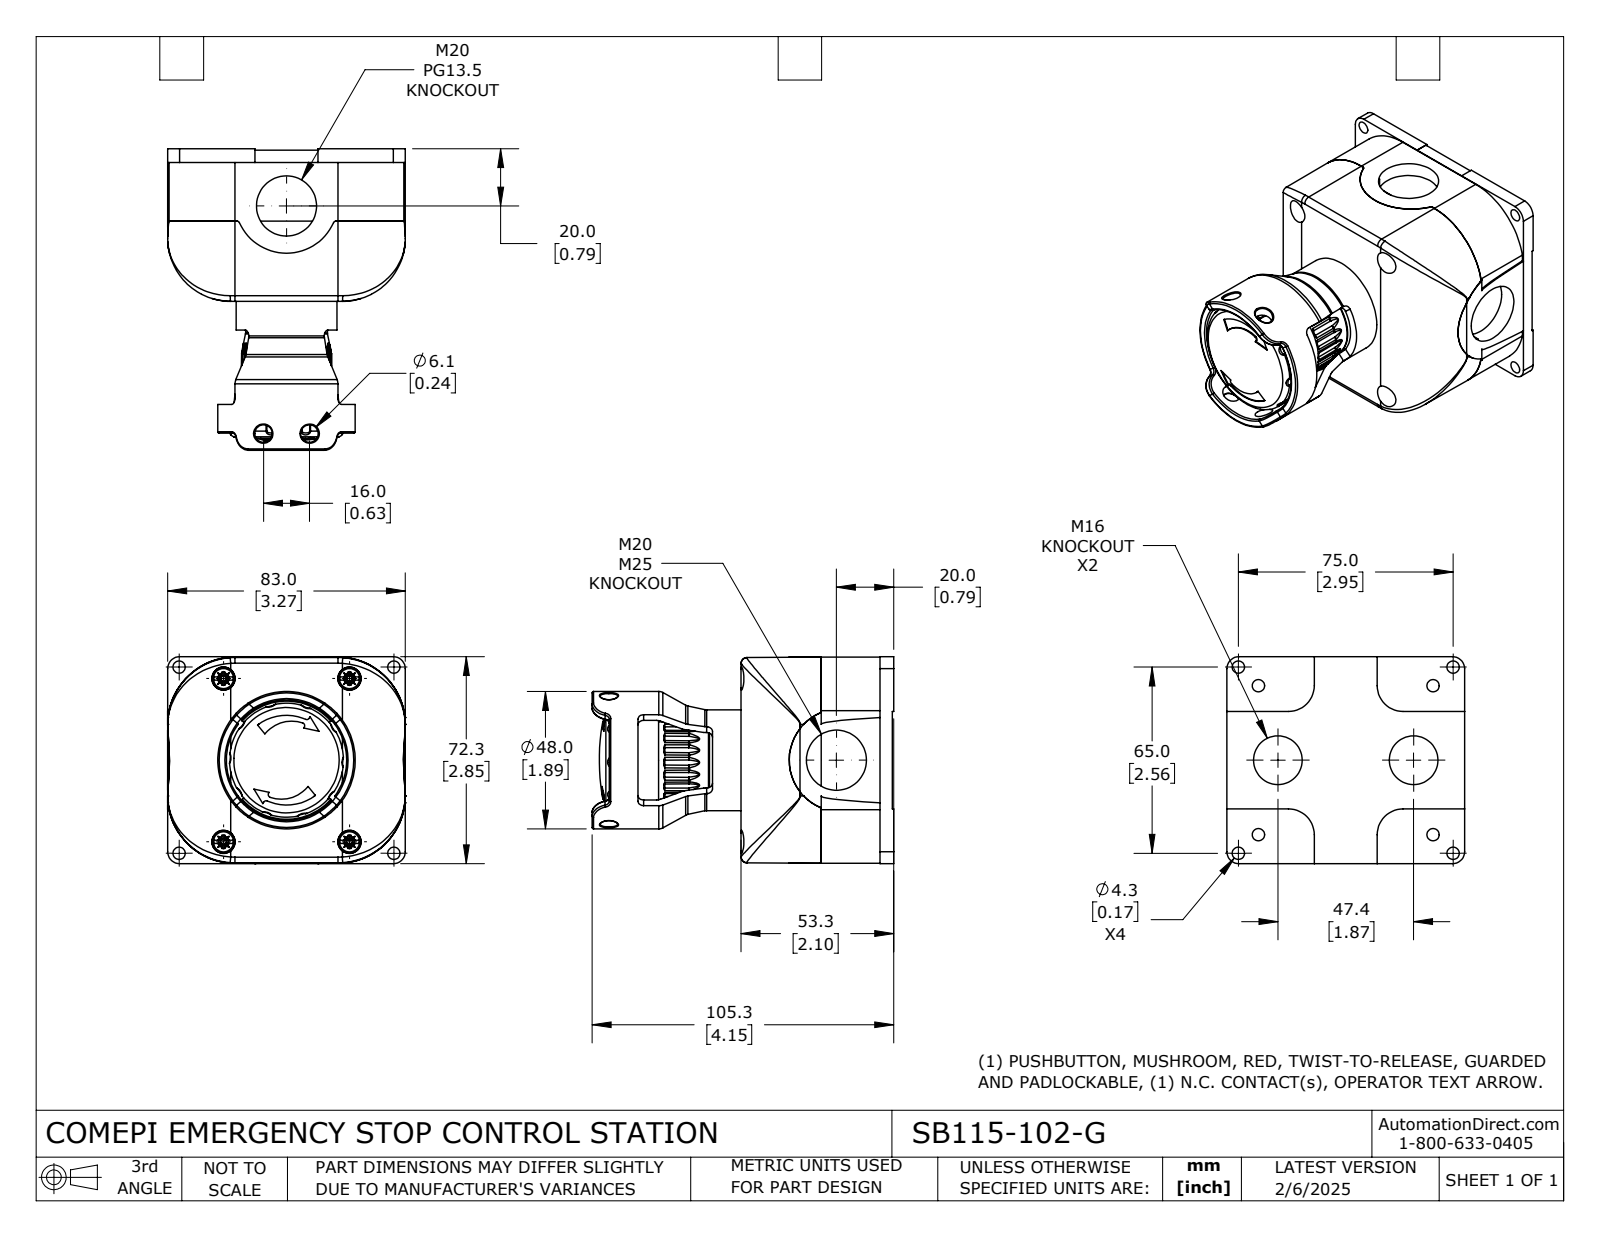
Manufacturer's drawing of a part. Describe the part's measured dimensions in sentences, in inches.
The part is named "SB115-102-G". Its 3-D file was written by "SolidWorks 2024 (CONFIG_CONTROL_DESIGN)". It is 6 solids with 1015 faces: 375 planar, 226 cylindrical and 414 other. Overall it measures 4.146 by 3.268 by 2.846 inches. Its volume is 15.13 cubic inches and its surface area 122.9 square inches. Round holes: 8 of diameter 0.169, 4 of diameter 0.323, 2 of diameter 0.24, 2 of diameter 0.669, 2 of diameter 0.827, 1 of diameter 0.051, 1 of diameter 0.713, 1 of diameter 0.854, 1 of diameter 1.15, 1 of diameter 1.24, 1 of diameter 1.654. Round bosses or shafts: 4 of diameter 0.276, 1 of diameter 1.89, 1 of diameter 1.386, 1 of diameter 1.142, 1 of diameter 0.925, 1 of diameter 0.874, 1 of diameter 0.843. Partial cylindrical surfaces (rounded edges, fillets, slot ends): 28 of radius 0.039, 16 of radius 0.079, 10 of radius 0.268, 4 of radius 0.035, 4 of radius 0.236, 4 of radius 0.354, 4 of radius 0.38, 4 of radius 0.925. The main face-to-face distances are 0.976, 0.098, 0.878, 2.079, 1.98, 1.102, 0.02, 0.118, 0.996, 2.098. The hole center spacings are 0.376, 1.058, 1.39, 1.578, 1.954, 2.32, 2.367, 2.689.
